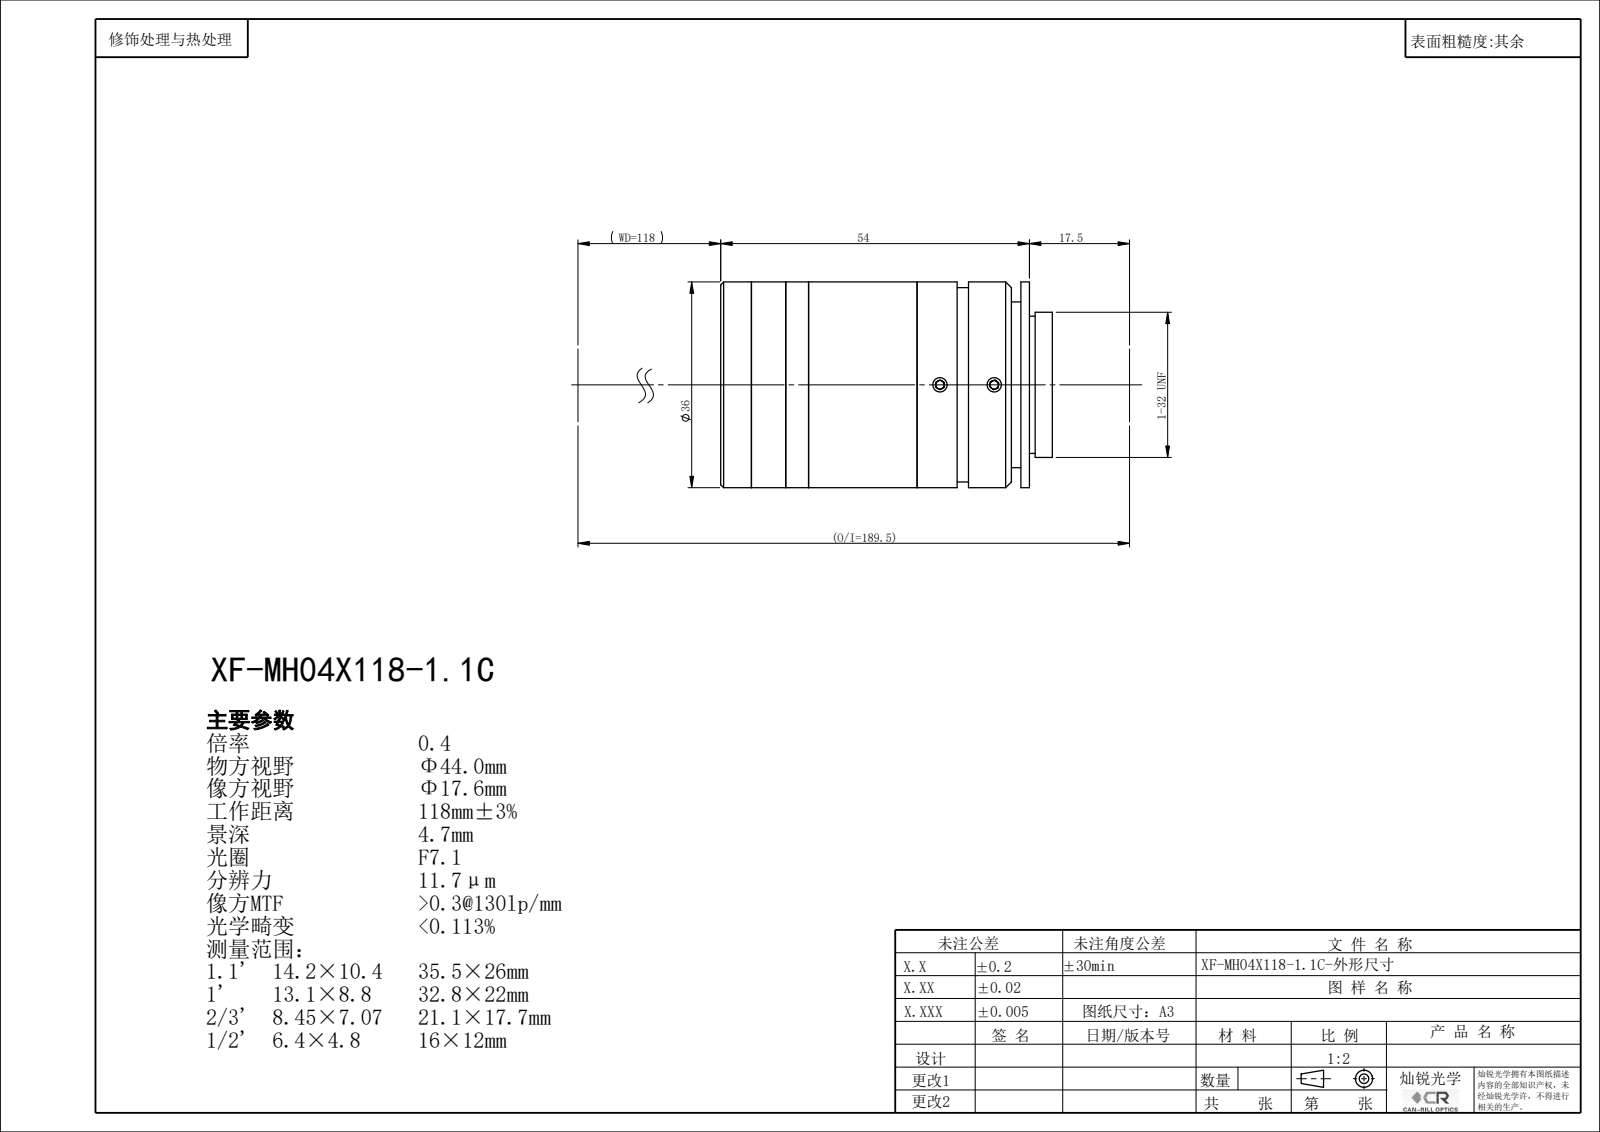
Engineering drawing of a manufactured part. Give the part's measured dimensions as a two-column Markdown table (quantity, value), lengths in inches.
| quantity | value |
| --- | --- |
| part name | XF-MH04X118-1.1C |
| STEP written by | SolidWorks 2022 (CONFIG_CONTROL_DESIGN) |
| units | inches |
| bodies | 0 solids, 138 faces (72 planar, 46 cylindrical, 20 other) |
| overall size | 2.285 × 1.417 × 1.417 |
| round holes (diameter × count) | 0.098 × 6, 0.591 × 1, 0.685 × 1, 0.882 × 1, 0.945 × 1, 0.98 × 1, 1.024 × 1, 1.039 × 1 |
| round bosses / shafts (diameter × count) | 1.417 × 1, 1.339 × 1, 1 × 1 |
| main face-to-face distances | 0.774, 1.354, 2.128, 0.059, 2.069, 0.715, 0.606, 0.748, 1.463, 1.522 |
| hole center spacings | 0.374 |
